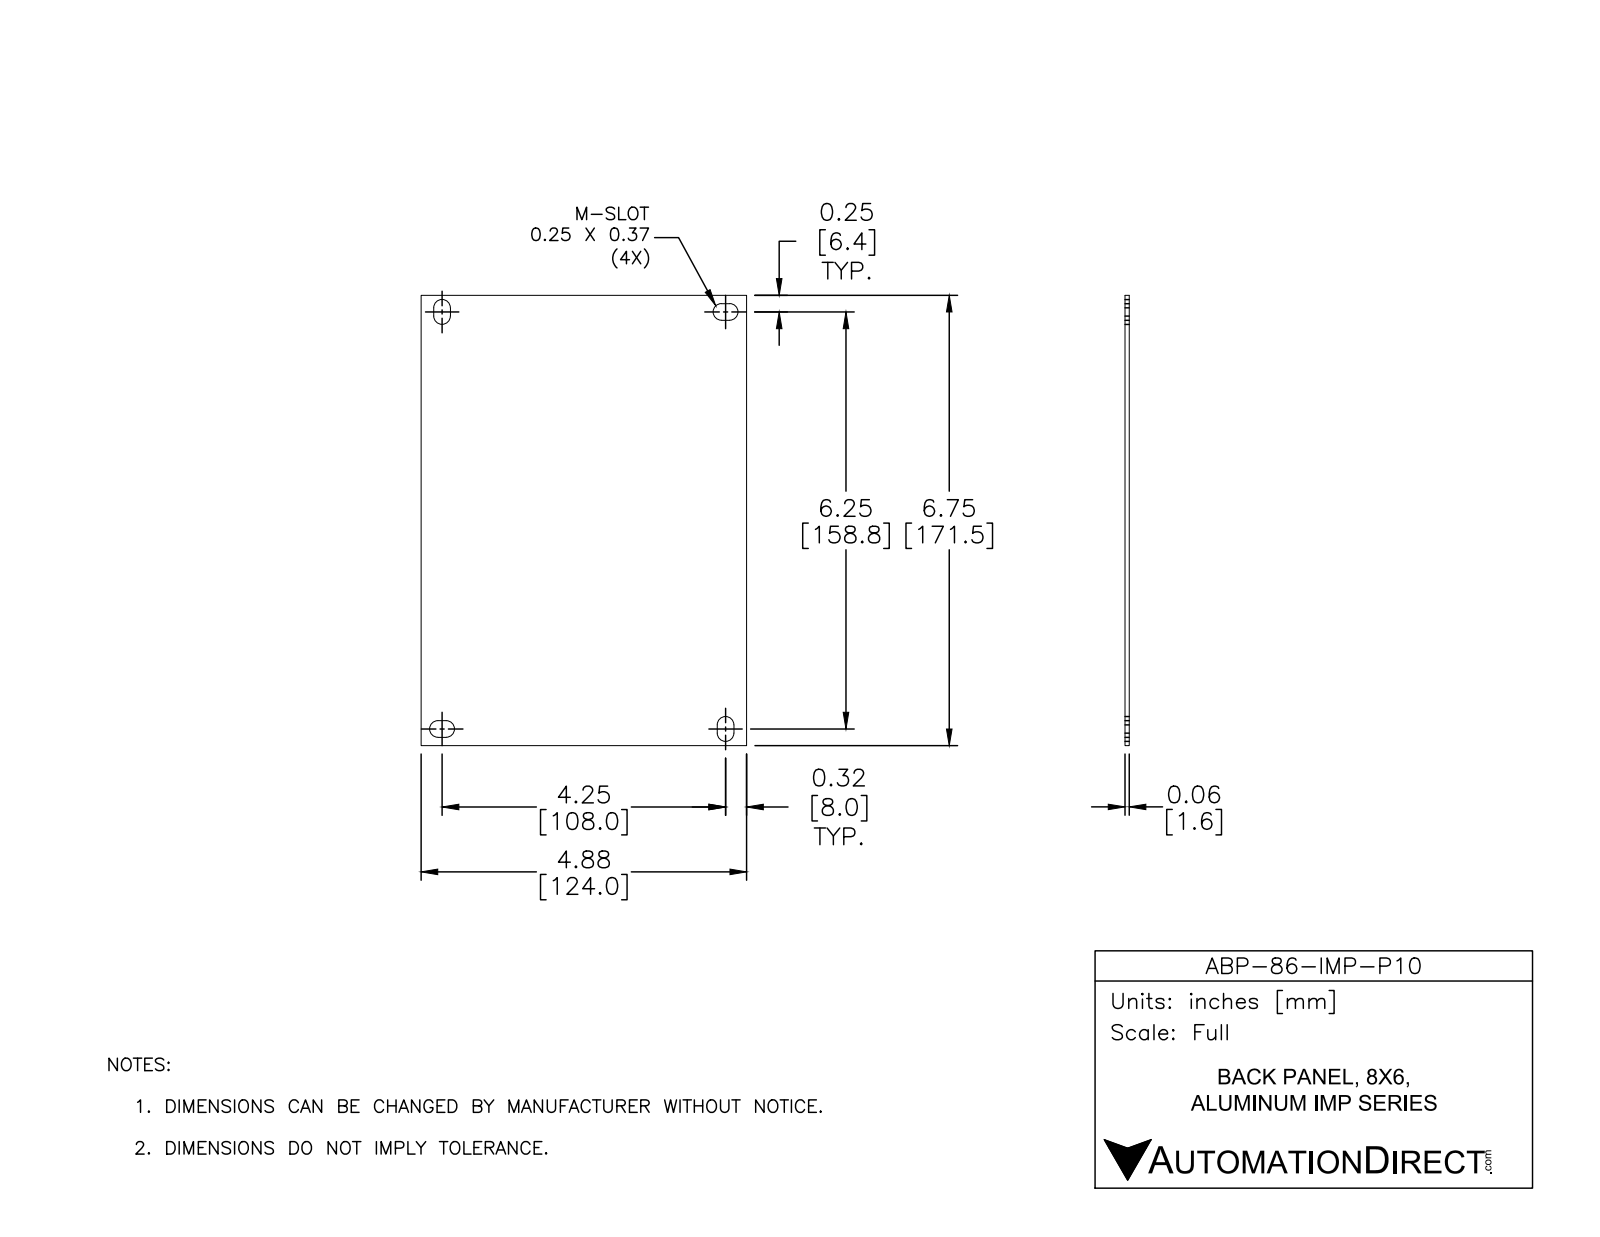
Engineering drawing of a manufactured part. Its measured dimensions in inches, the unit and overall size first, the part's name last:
Units: inches
Overall size (bounding box): 6.75 × 4.88 × 0.064
Partial cylindrical surfaces — rounded edges, fillets, slot ends (radius × count): R0.125 ×8
Main face-to-face distances: 0.064, 4.88, 6.75, 0.25, 0.125, 6.625, 4.25, 0.375, 6.375, 6.375
Volume: 2.091 in³ · Surface area: 67 in²
Bodies: 1 solid, 24 faces (14 planar, 10 cylindrical, 0 other)
Part name (STEP PRODUCT): ABP-86-IMP-P604
STEP written by: SolidWorks 2016 (AUTOMOTIVE_DESIGN)
